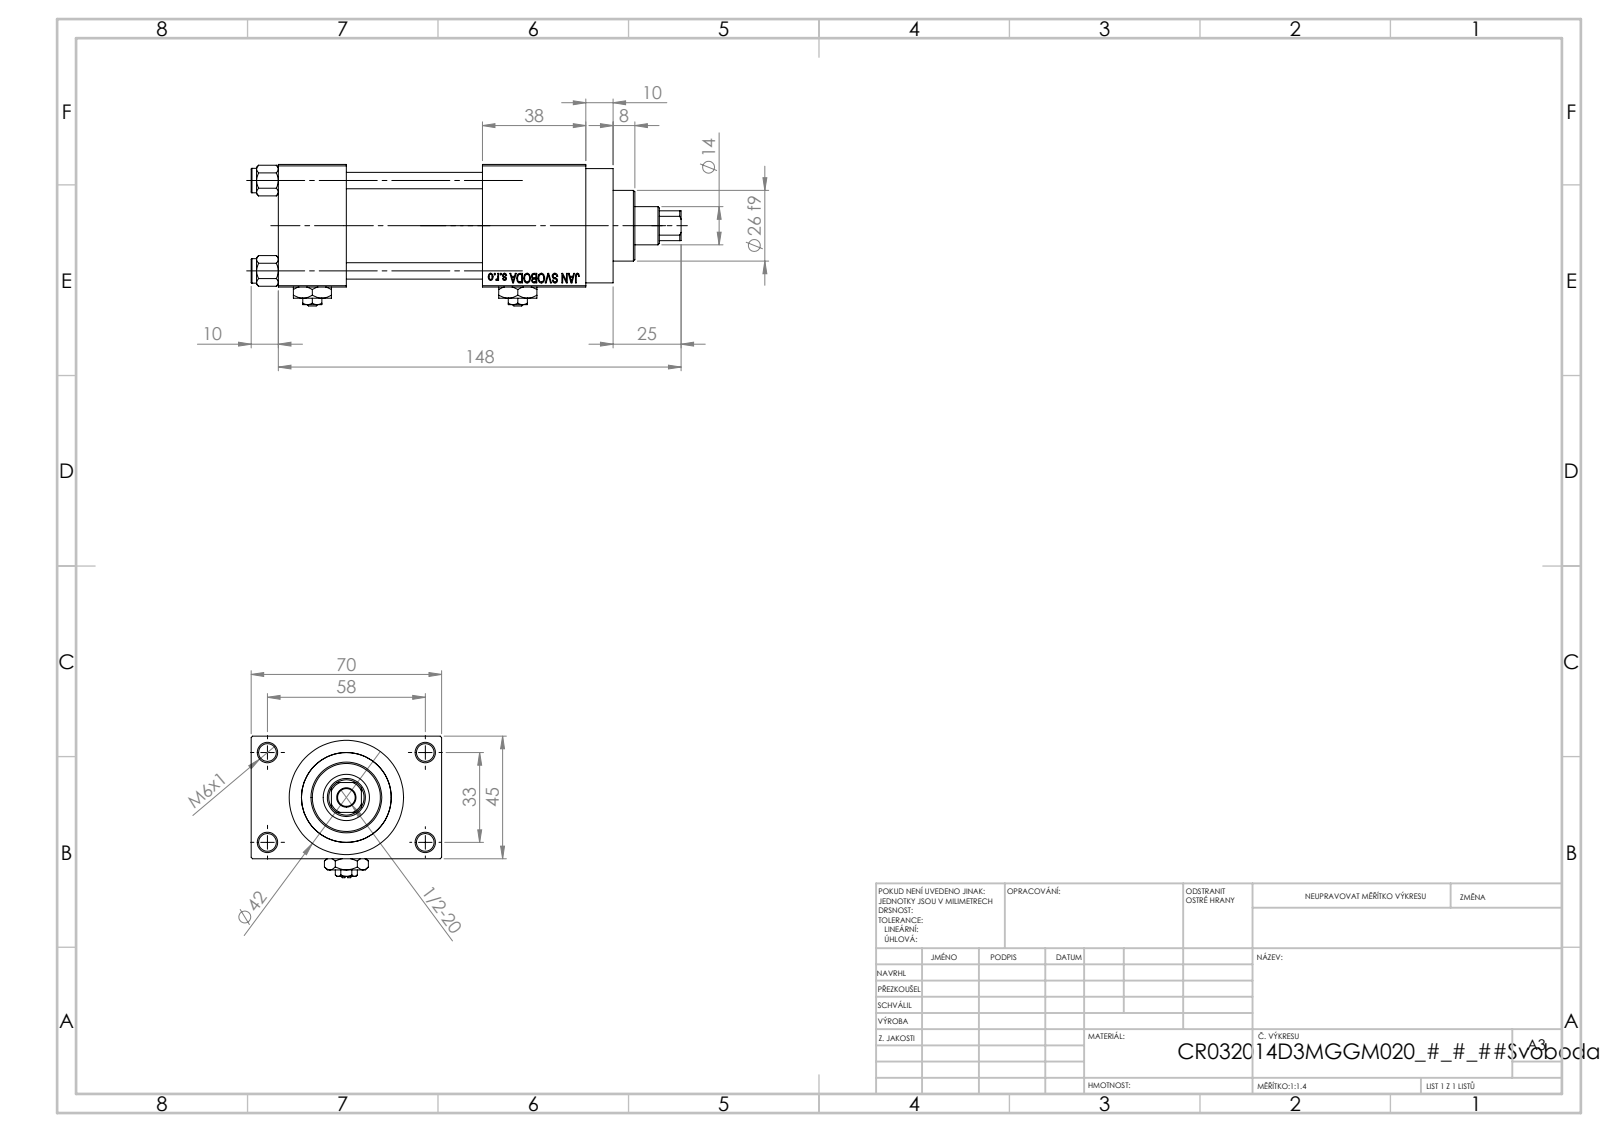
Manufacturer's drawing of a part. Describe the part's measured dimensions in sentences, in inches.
The part is named "V215CR_D_TYCINKA; Zatka_pro_OIL_PORT; V215_VC_A; NUT_M5_D (+2 more)". Its 3-D file was written by "SolidWorks 2019 (CONFIG_CONTROL_DESIGN)". It is 13 solids with 1202 faces: 542 planar, 100 cylindrical and 560 other. Overall it measures 6.22 by 2.756 by 2.047 inches. Its volume is 14.08 cubic inches and its surface area 118.8 square inches. Round holes: 5 of diameter 0.256, 4 of diameter 0.236, 2 of diameter 0.276, 2 of diameter 0.518, 2 of diameter 0.787, 1 of diameter 0.551, 1 of diameter 0.669, 1 of diameter 0.945, 1 of diameter 1.26, 1 of diameter 1.299. Round bosses or shafts: 4 of diameter 0.354, 1 of diameter 1.654, 1 of diameter 1.496, 1 of diameter 1.024. Partial cylindrical surfaces (rounded edges, fillets, slot ends): 1 of radius 0.256. The main face-to-face distances are 1.772, 0.984, 0.492, 2.264, 1.969, 2.953, 3.465, 2.756, 1.496, 4.449. The hole center spacings are 0.488, 0.924, 1.307, 1.314, 1.392, 1.795, 2.219, 1.299.
